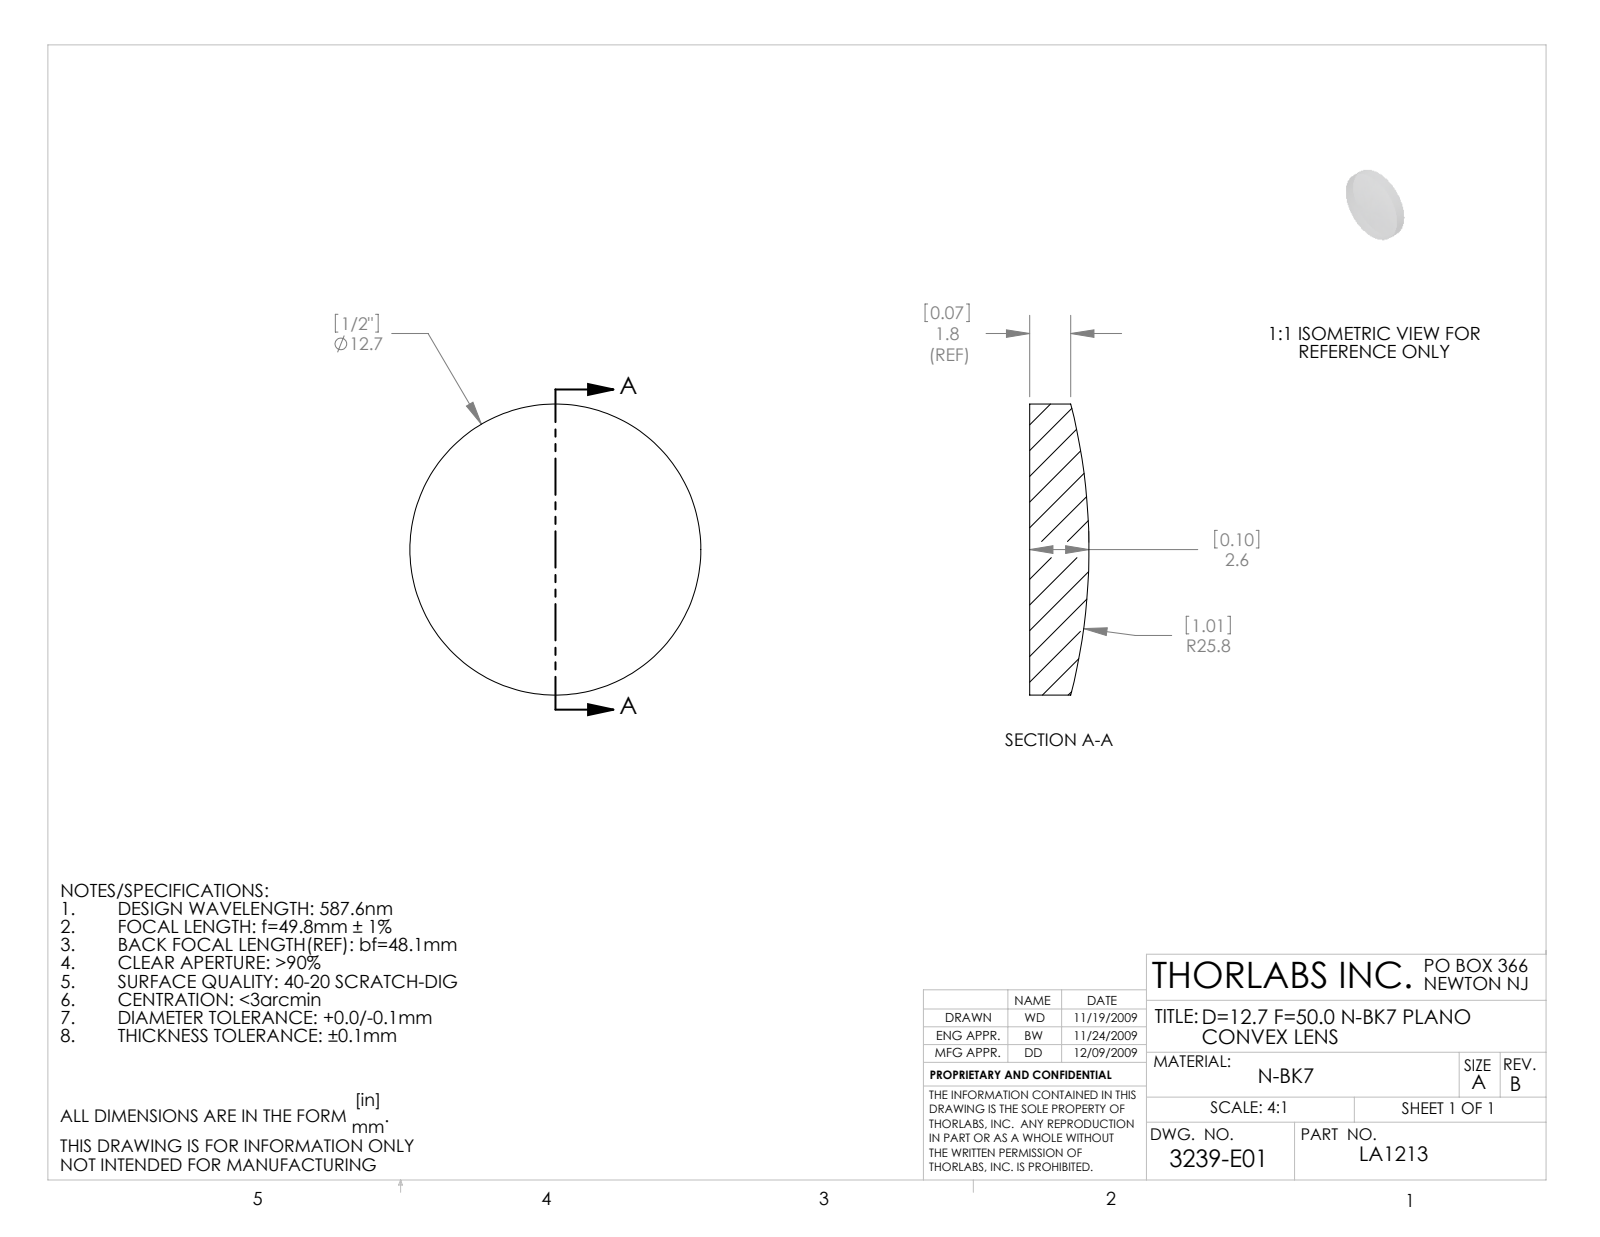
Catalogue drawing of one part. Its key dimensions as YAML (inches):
part_name: "3239-E0W"
step_written_by: "SolidWorks 2009 (AUTOMOTIVE_DESIGN)"
units: inches
bodies: {solids: 1, faces: 5, planar: 1, cylindrical: 2, other: 2}
overall_size: [0.5, 0.5, 0.102]
volume: 0.017
surface_area: 0.507
round_bosses_or_shafts:
  - {diameter: 0.5, count: 1}
